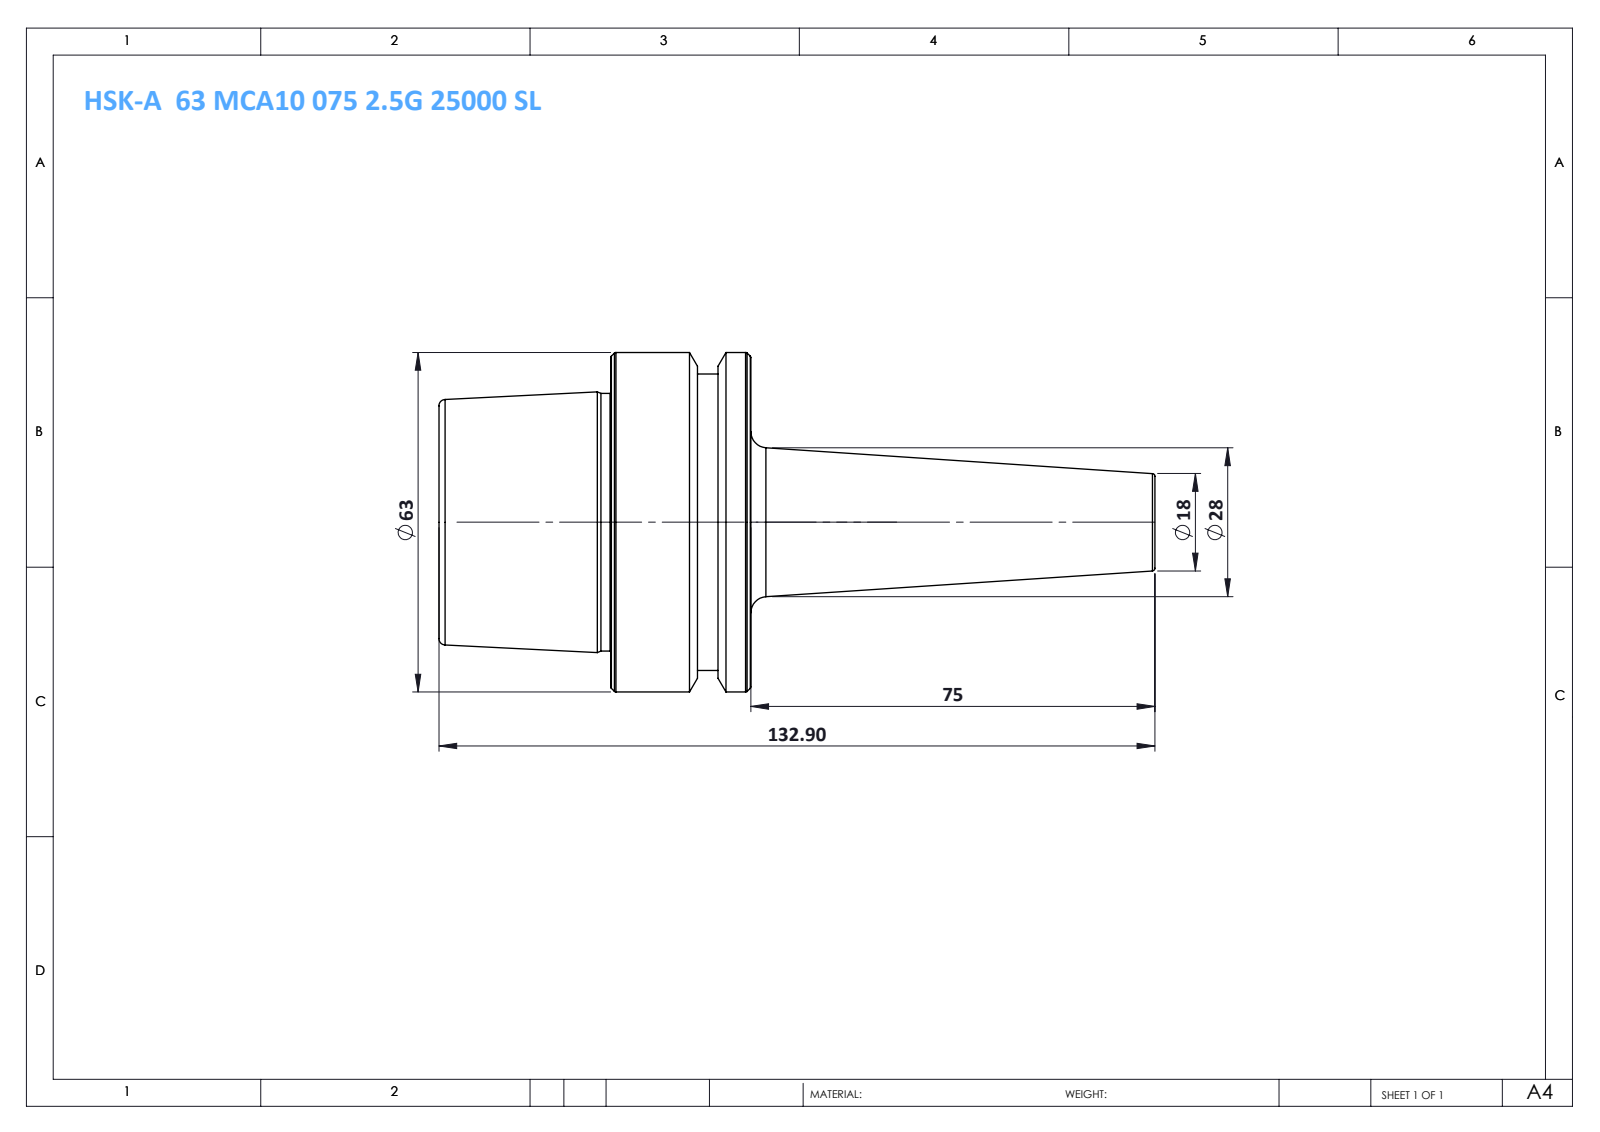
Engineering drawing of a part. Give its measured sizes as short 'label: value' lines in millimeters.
name: HSK-A 63 MCA10 075 2.5G 25000 SL
written by: SolidWorks 2014 (CONFIG_CONTROL_DESIGN)
unit: mm
bodies: 1 solid, 46 faces (6 planar, 8 cylindrical, 32 other)
size: 132.9 × 63 × 63
volume: 164 396 mm³; area: 21 615 mm²
bosses: 1× ⌀63, 1× ⌀55, 1× ⌀47.78
face distances: 57.9, 26, 31.9, 6.1, 19.9, 51.8, 9.9, 3.8, 16.1, 48
